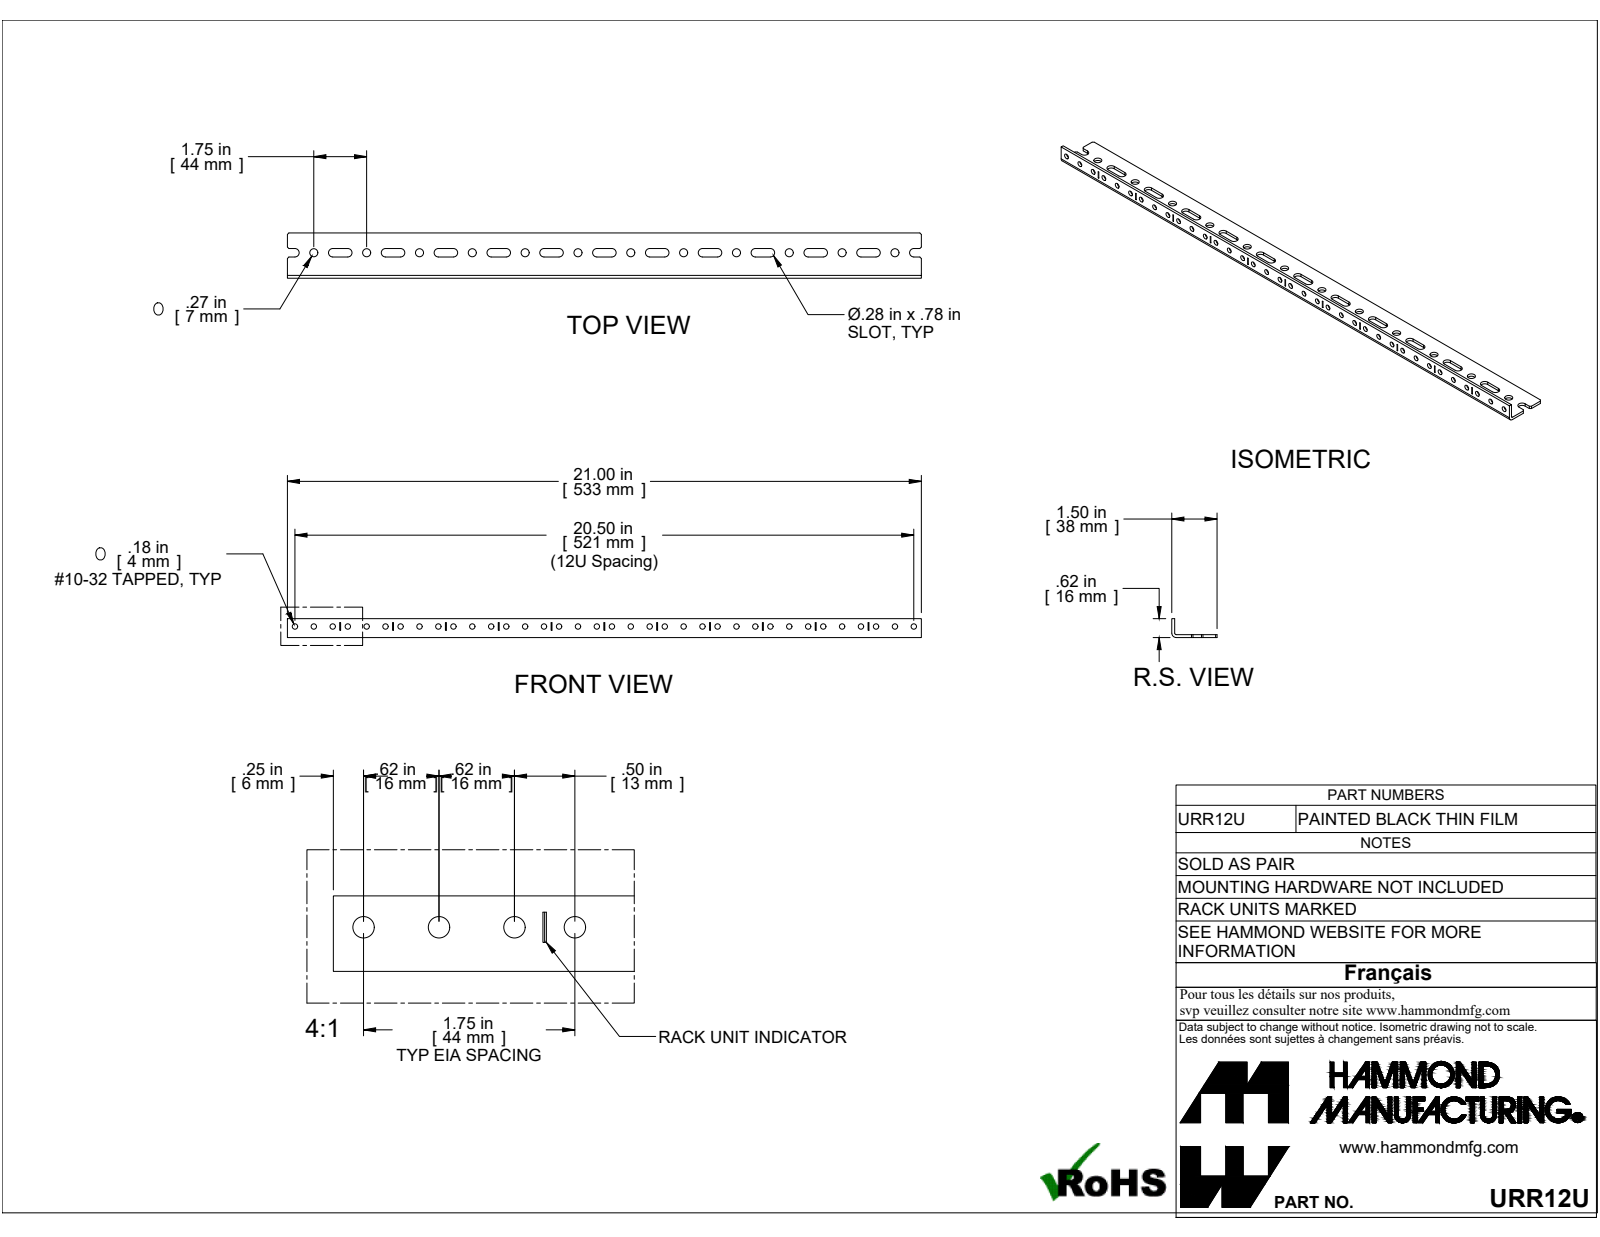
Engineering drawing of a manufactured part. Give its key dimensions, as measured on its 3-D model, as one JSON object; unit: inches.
{"part_name": "COM57213-12", "step_written_by": "ST-DEVELOPER v16.7 (AUTOMOTIVE_DESIGN)", "units": "inches", "bodies": {"solids": 1, "faces": 160, "planar": 86, "cylindrical": 74, "other": 0}, "overall_size": [21, 1.5, 0.625], "volume_in3": 3.588, "surface_area_in2": 84.94, "round_holes": [[0.177, 36], [0.266, 12]], "partial_cylinders_radius": [[0.141, 24], [0.048, 1], [0.143, 1]], "face_to_face_distances": [0.095, 0.625, 0.53, 1.5, 1.405, 0.702, 0.983, 0.607, 0.889, 0.281], "hole_center_spacings": [3.5, 1.75, 7, 5.25, 10.5, 0.625, 0.625, 1.125]}
